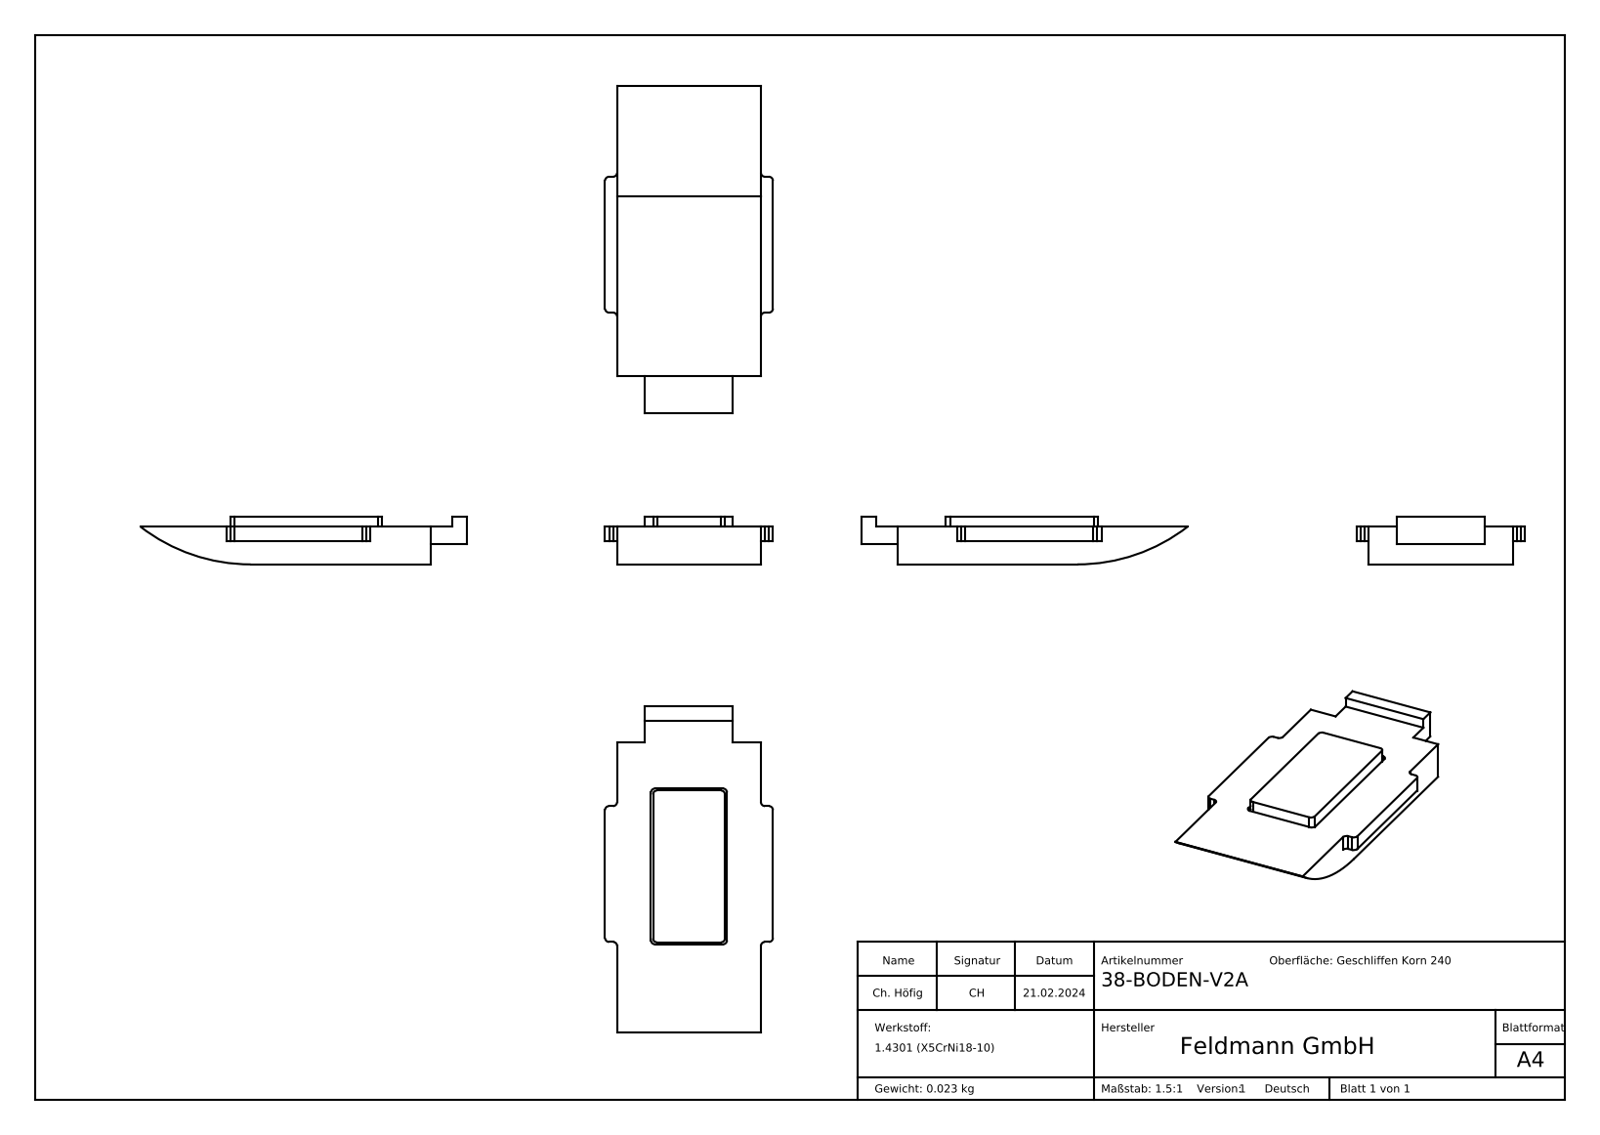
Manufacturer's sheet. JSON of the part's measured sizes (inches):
{"part_name": "38-BODEN-V2A; 38-Boden-GU_38-BODEN-ZN0-GU; 38-Boden-XXX-OG_38-BODEN-V2A Teil1", "step_written_by": "SolidWorks 2018 (CONFIG_CONTROL_DESIGN)", "units": "inches", "bodies": {"solids": 2, "faces": 356, "planar": 210, "cylindrical": 17, "other": 129}, "overall_size": [1.608, 0.827, 0.236], "volume_in3": 0.193, "surface_area_in2": 3.799, "partial_cylinders_radius": [[0.02, 16], [0.886, 1]], "face_to_face_distances": [0.187, 0.167, 0.02, 0.236, 0.069, 0.049, 0.709, 0.138, 0.073, 0.768]}
